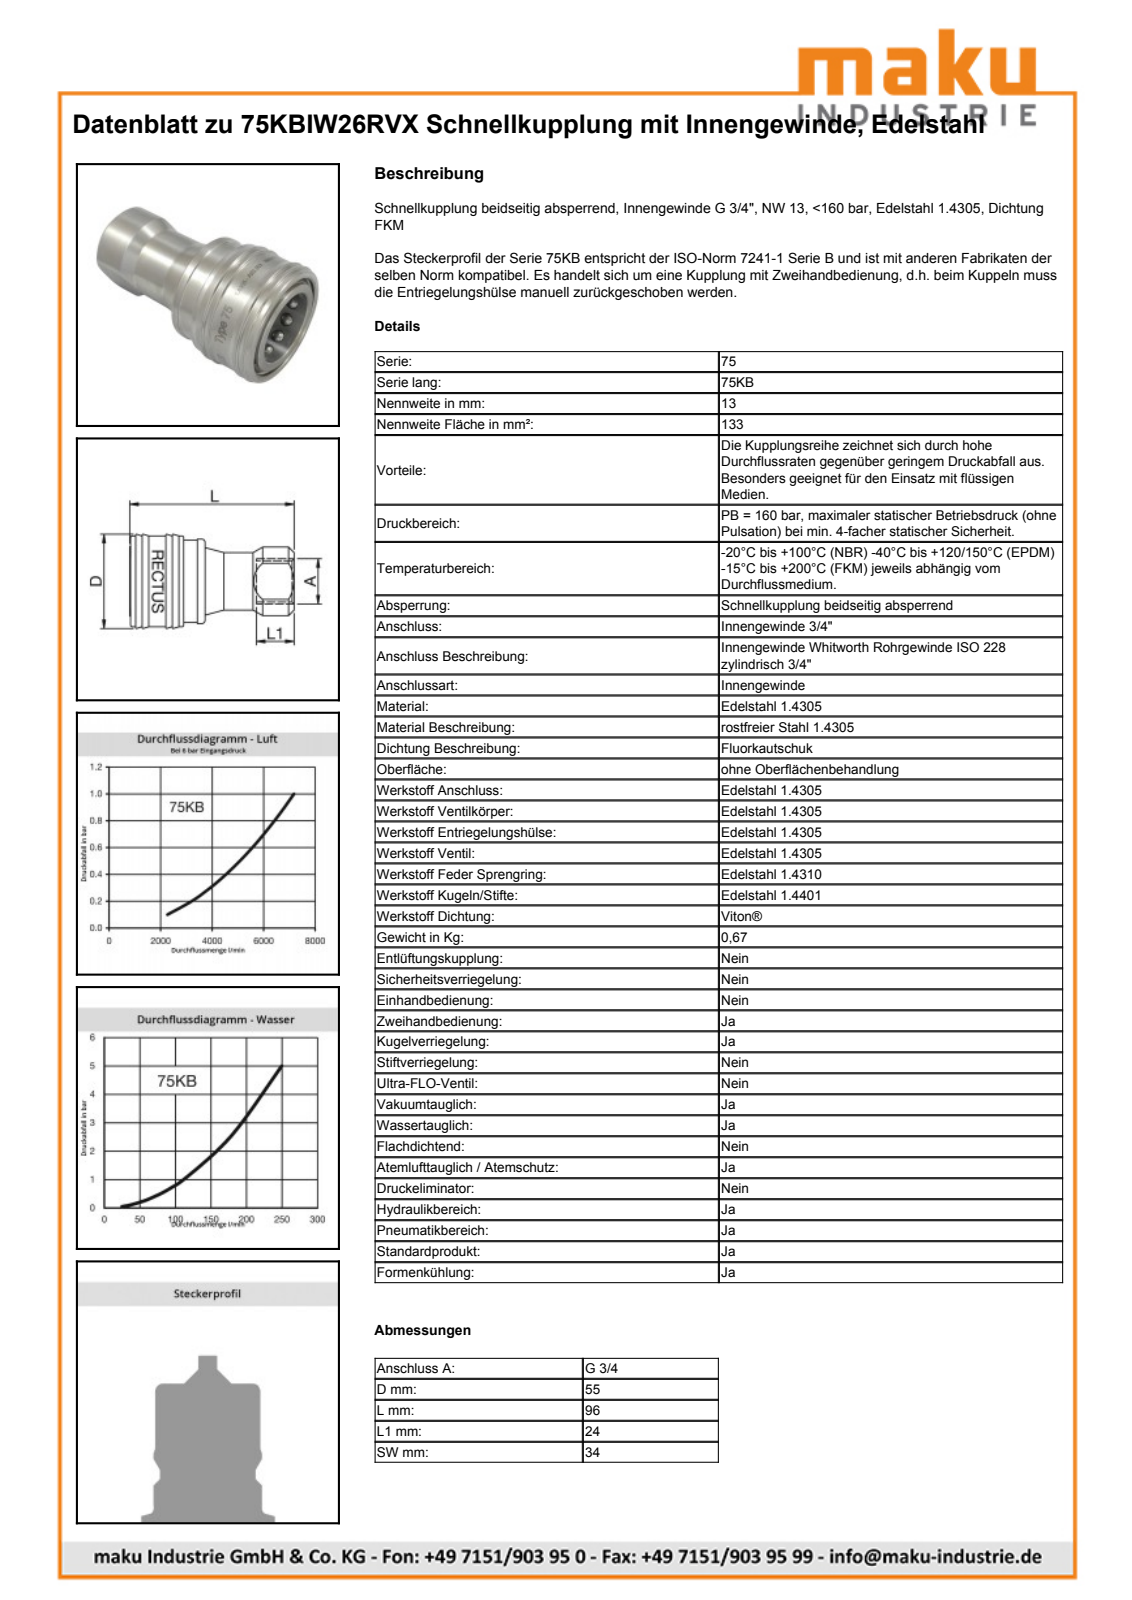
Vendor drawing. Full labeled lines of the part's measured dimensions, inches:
Part name (STEP PRODUCT): D110803
STEP written by: Autodesk Inventor 2013 (AUTOMOTIVE_DESIGN)
Units: inches
Bodies: 1 solid, 845 faces (326 planar, 94 cylindrical, 425 other)
Overall size (bounding box): 3.78 × 2.168 × 2.168
Volume: 7.466 in³ · Surface area: 51.35 in²
Round holes (diameter × count): ⌀0.965 ×1, ⌀1.48 ×1, ⌀1.642 ×1, ⌀1.811 ×1, ⌀1.902 ×1
Round bosses / shafts (diameter × count): ⌀2.087 ×1, ⌀1.941 ×1, ⌀1.89 ×1, ⌀1.626 ×1, ⌀1.528 ×1, ⌀1.383 ×1, ⌀1.319 ×1
Partial cylindrical surfaces — rounded edges, fillets, slot ends (radius × count): R0.787 ×1, R1.039 ×1
Main face-to-face distances: 1.339, 1.161, 0.394, 2.796, 1.634, 2.402, 0.768, 0.177, 1.063, 0.571
